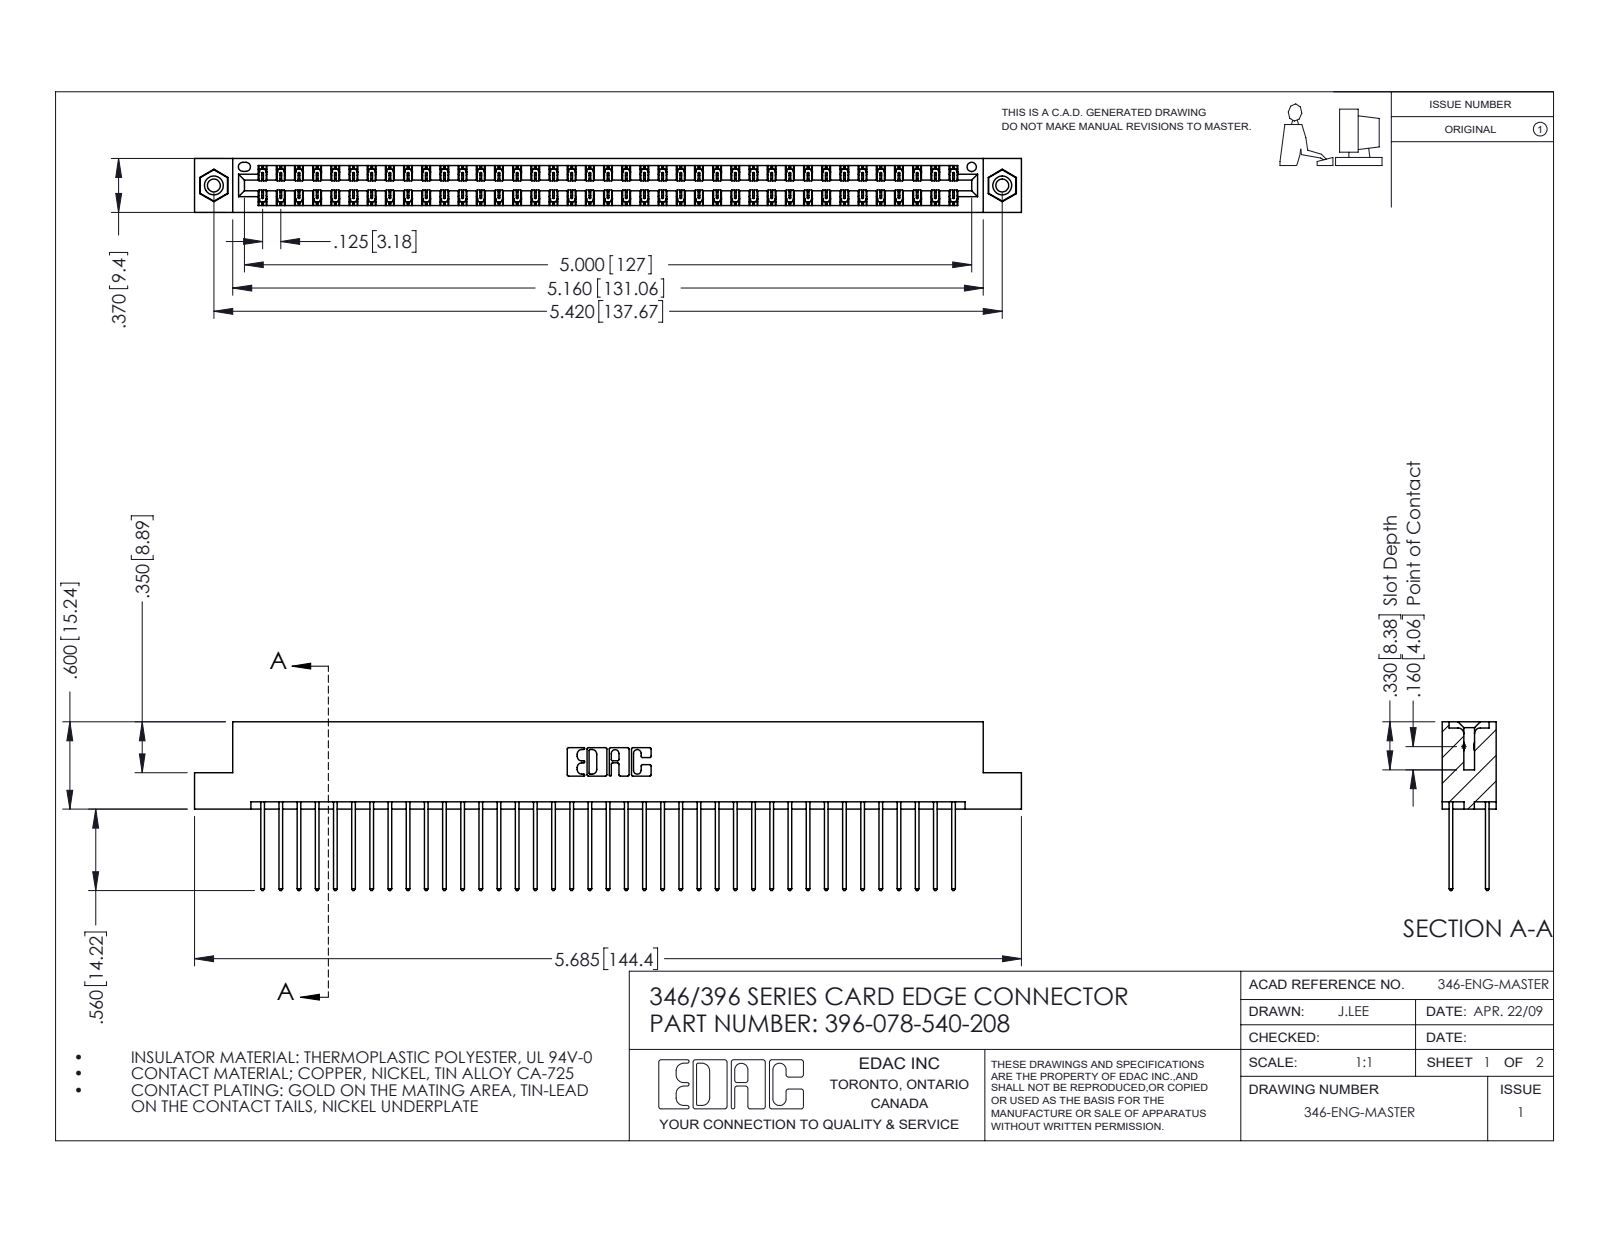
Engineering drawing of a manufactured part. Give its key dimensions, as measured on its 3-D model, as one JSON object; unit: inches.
{"part_name": "345-250-001_345-250-003-102; 396-078-540-208; 346 Part_Flush Mounting Lugs - 0.156 Dia-TI; 345-292-001_345-293-140", "step_written_by": "SolidWorks 2016 (CONFIG_CONTROL_DESIGN)", "units": "inches", "bodies": {"solids": 81, "faces": 4238, "planar": 2838, "cylindrical": 1384, "other": 16}, "overall_size": [5.685, 1.16, 0.37], "volume_in3": 0.875, "surface_area_in2": 32.69, "round_holes": [[0.089, 2], [0.125, 2], [0.156, 2], [0.064, 1]], "round_bosses_or_shafts": [[0.155, 2]], "partial_cylinders_radius": [[0.006, 117], [0.01, 78], [0.01, 22], [0.007, 6], [0.031, 6], [0.026, 3], [0.014, 2], [0.022, 2]], "face_to_face_distances": [0.048, 0.322, 0.25, 0.072, 0.298, 0.025, 0.37, 0.275, 0.148, 0.222], "hole_center_spacings": [0.246, 5.211, 5.42]}
